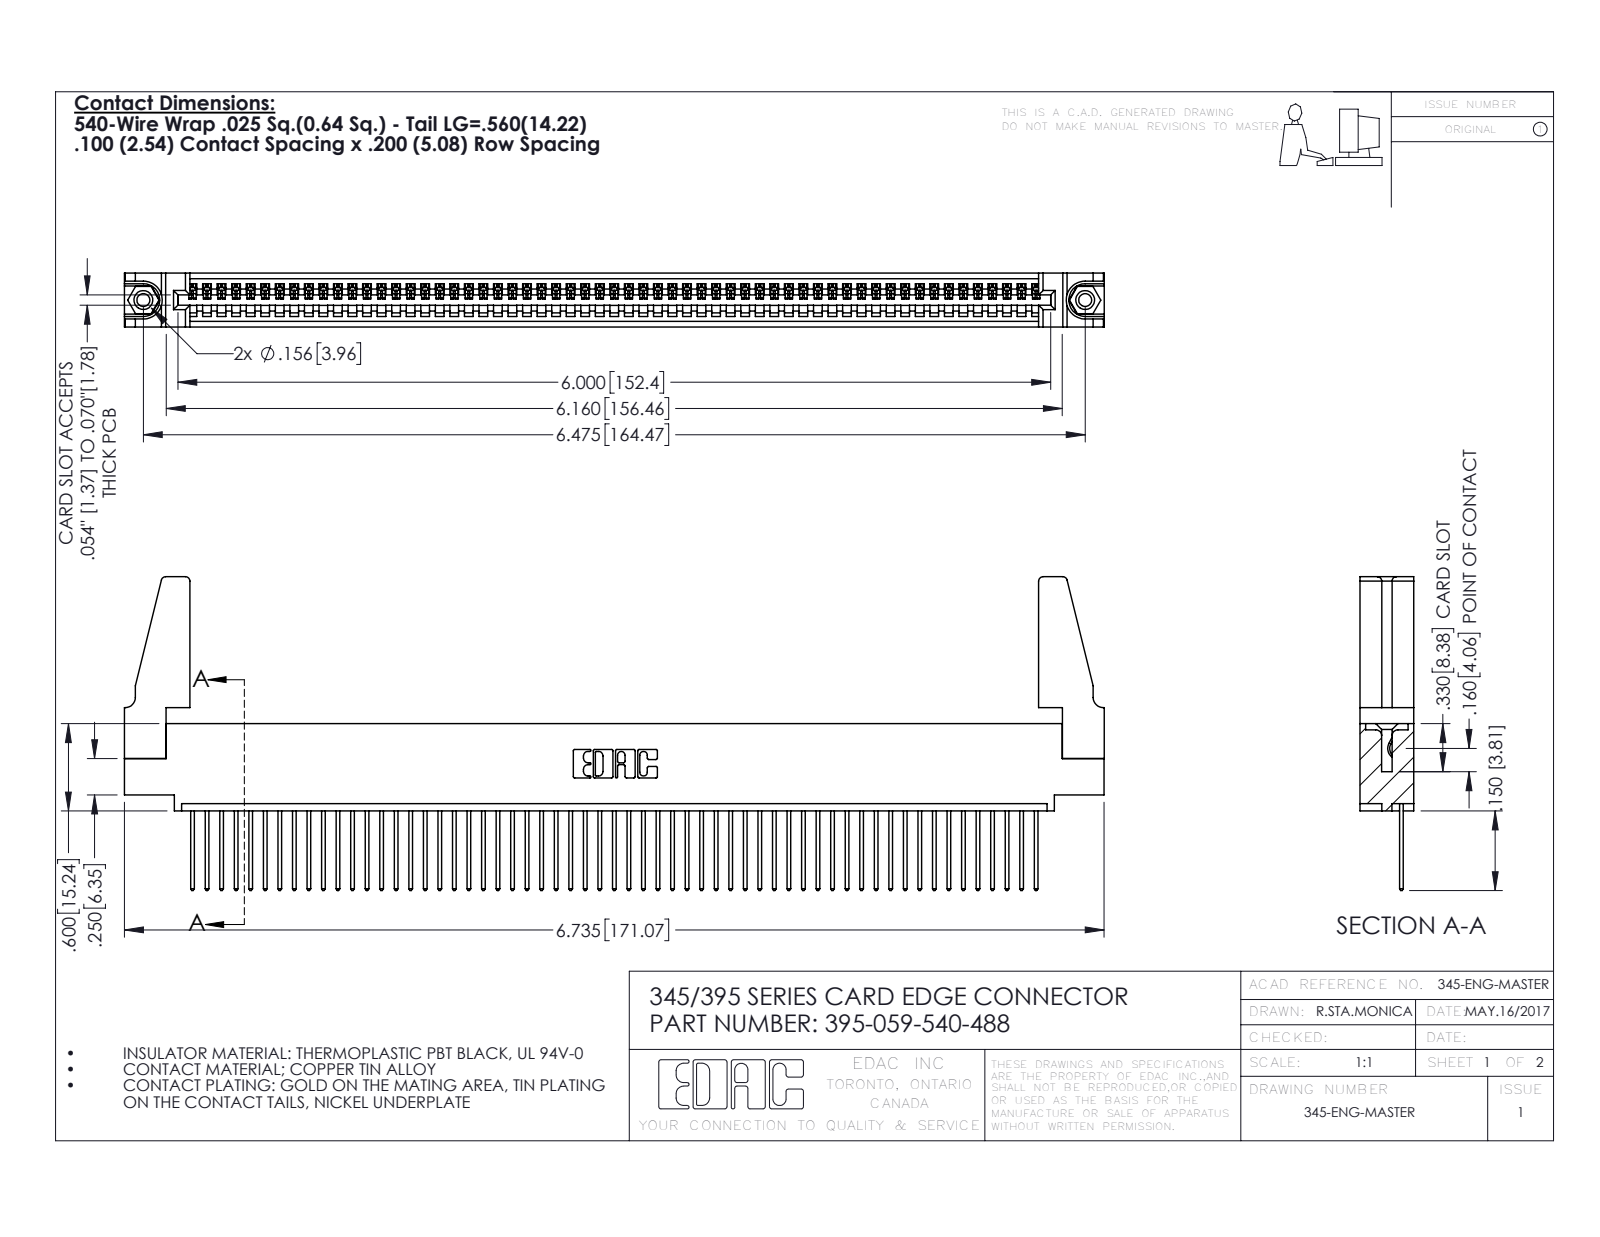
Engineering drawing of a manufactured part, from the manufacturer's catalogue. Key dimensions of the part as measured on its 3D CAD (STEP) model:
Part name (STEP PRODUCT): 345-250-001_345-250-001-102; 345-220-078_345-220-088; 345-292-001_345-293-140; 345 Part_0.110 Offset - 0.156 Dia-TH (+1 more)
STEP written by: SolidWorks 2016 (CONFIG_CONTROL_DESIGN)
Units: inches
Bodies: 64 solids, 3676 faces (2516 planar, 1144 cylindrical, 16 other)
Overall size (bounding box): 6.736 × 2.157 × 0.37
Volume: 1.199 in³ · Surface area: 40 in²
Round holes (diameter × count): ⌀0.089 ×2, ⌀0.125 ×2, ⌀0.156 ×2, ⌀0.064 ×1
Round bosses / shafts (diameter × count): ⌀0.155 ×2
Partial cylindrical surfaces — rounded edges, fillets, slot ends (radius × count): R0.006 ×118, R0.01 ×118, R0.01 ×22, R0.03 ×8, R0.007 ×6, R0.031 ×6, R0.026 ×3, R0.031 ×2
Main face-to-face distances: 0.072, 0.298, 0.37, 0.098, 0.272, 0.025, 0.2, 0.225, 0.149, 0.072
Hole centre spacings: 0.27, 6.239, 6.475
